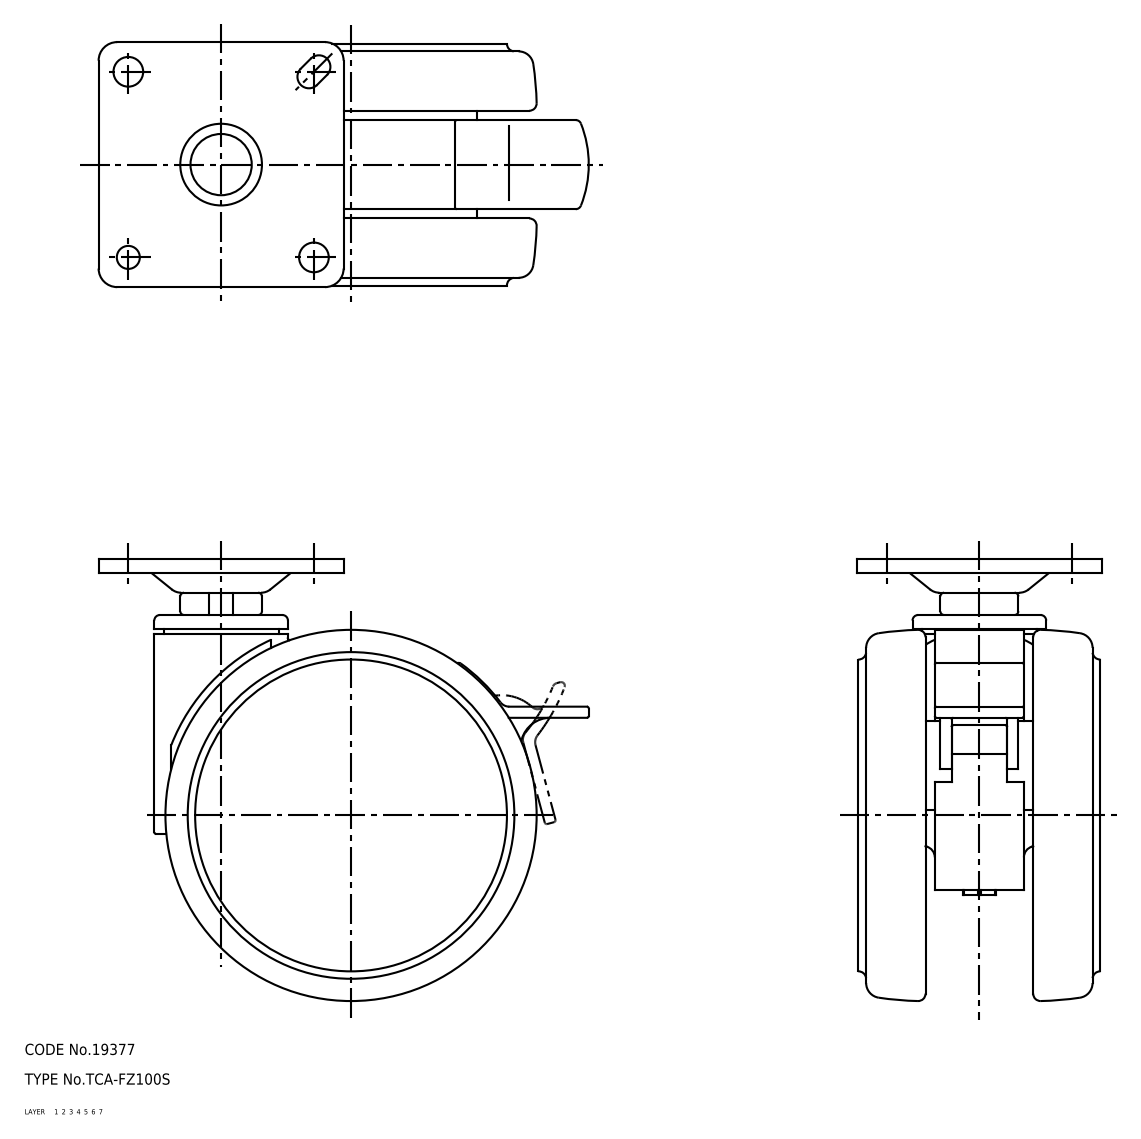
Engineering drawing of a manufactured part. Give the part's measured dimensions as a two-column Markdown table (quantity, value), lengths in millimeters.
| quantity | value |
| --- | --- |
| part name | TCA-FZ100S; caster |
| STEP written by | SolidWorks 2015 (AUTOMOTIVE_DESIGN) |
| units | millimeters |
| bodies | 1 solid, 2528 faces (874 planar, 1205 cylindrical, 449 other) |
| overall size | 132.03 × 119 × 66 |
| volume | 318 166 mm³ |
| surface area | 133 654 mm² |
| round holes (diameter × count) | 8 × 2, 2.8 × 1, 3 × 1, 3.3 × 1, 4.1 × 1, 4.2 × 1, 6 × 1, 6.2 × 1, 9.1 × 1, 10 × 1, 10.1 × 1, 10.5 × 1 |
| round bosses / shafts (diameter × count) | 87.8 × 1, 36 × 1, 31 × 1, 27.9 × 1, 27.6 × 1, 22 × 1, 20 × 1, 19 × 1 |
| partial cylindrical surfaces (radius × count) | 0.5 × 236, 1.2 × 160, 1 × 87, 2 × 25, 1.5 × 23, 0.2 × 18, 0.3 × 12, 3 × 8 |
| main face-to-face distances | 1.8, 61.6, 63.4, 3.6, 59.8, 14.5, 16.3, 45.3, 18.1, 47.1 |
| hole center spacings | 35.36, 50, 22.78, 29.45, 44, 70.71 |
